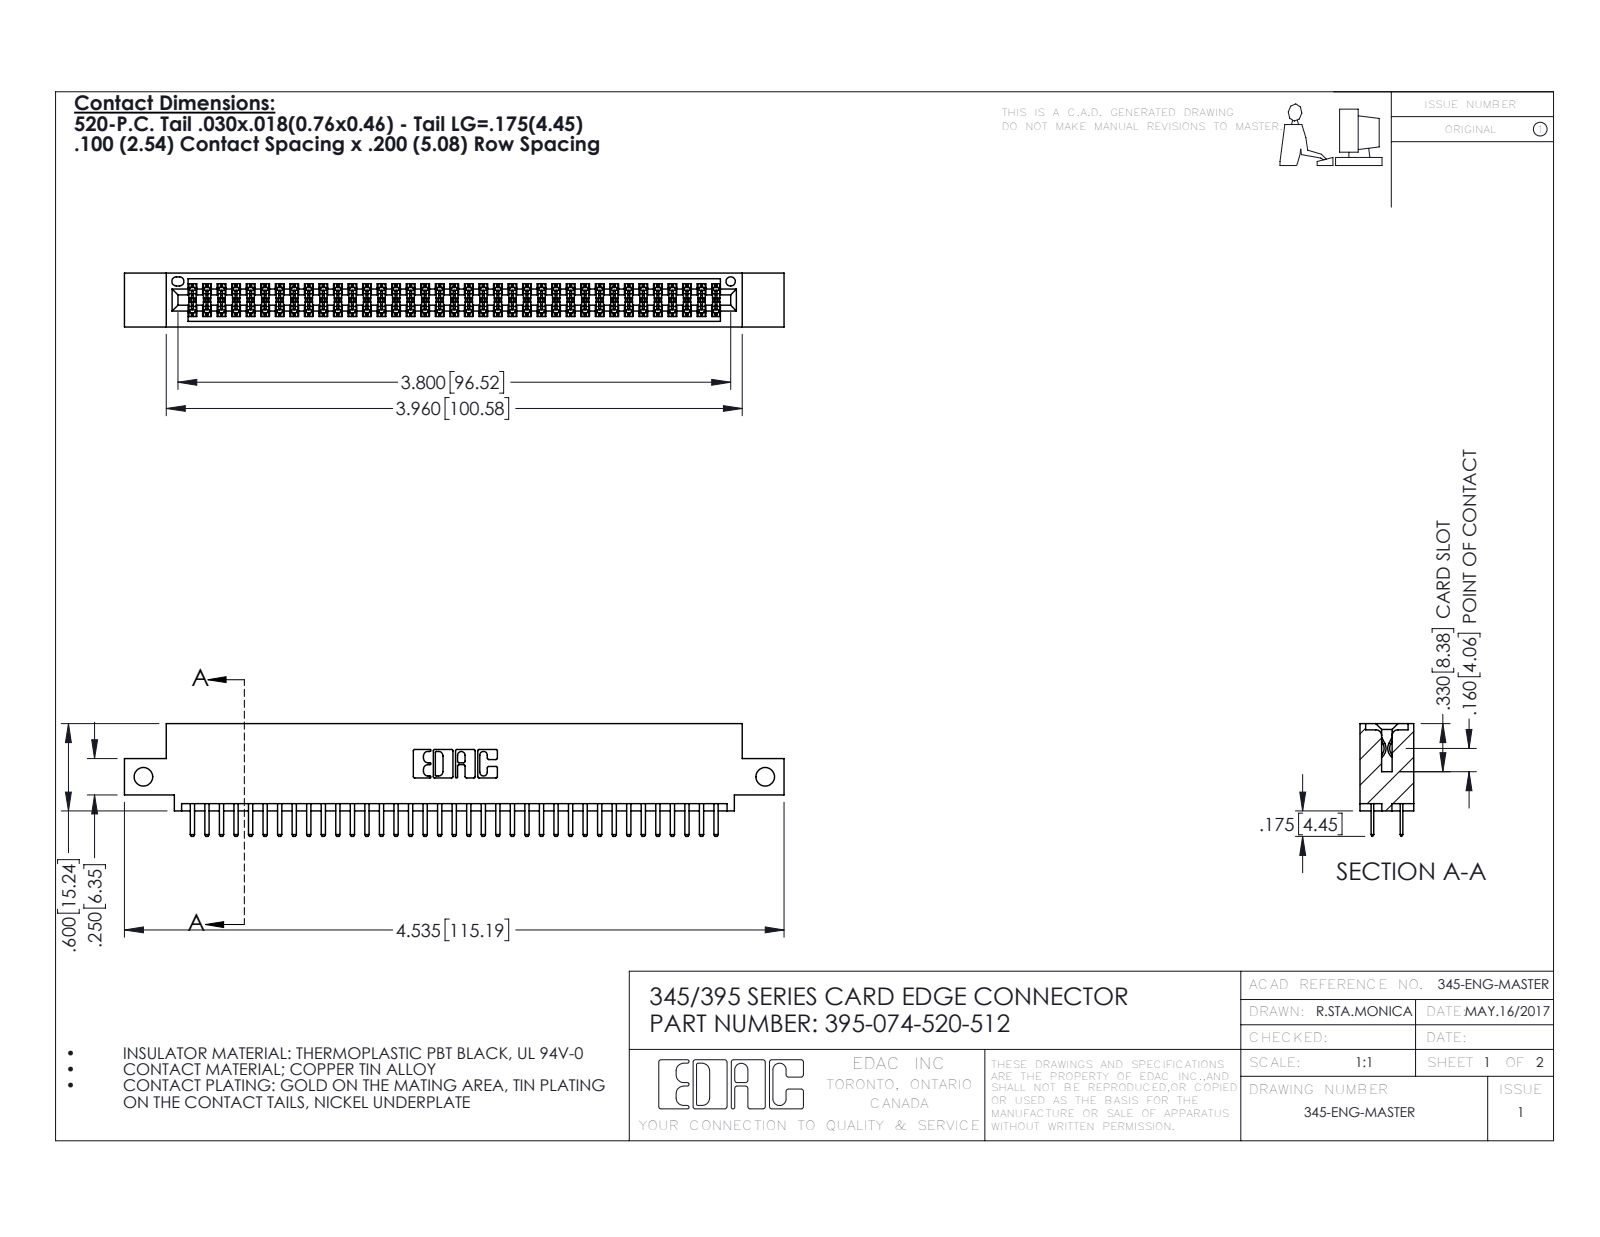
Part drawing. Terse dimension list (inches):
name: 395-074-520-512; 345 Part_0.110 Offset - Side Mount; 345-292-001_345-293-120
written by: SolidWorks 2016 (CONFIG_CONTROL_DESIGN)
unit: in
bodies: 75 solids, 4126 faces (2674 planar, 1452 cylindrical, 0 other)
size: 4.535 × 0.775 × 0.37
volume: 0.668 in³; area: 24.76 in²
holes: 2× ⌀0.128, 1× ⌀0.064
rounds: 111× R0.006, 78× R0.01, 22× R0.01, 6× R0.007, 6× R0.031, 3× R0.026, 2× R0.014, 2× R0.019
face distances: 0.298, 0.072, 0.2, 0.37, 0.098, 0.272, 0.025, 0.225, 0.022, 0.072
hole spacings: 4.275
